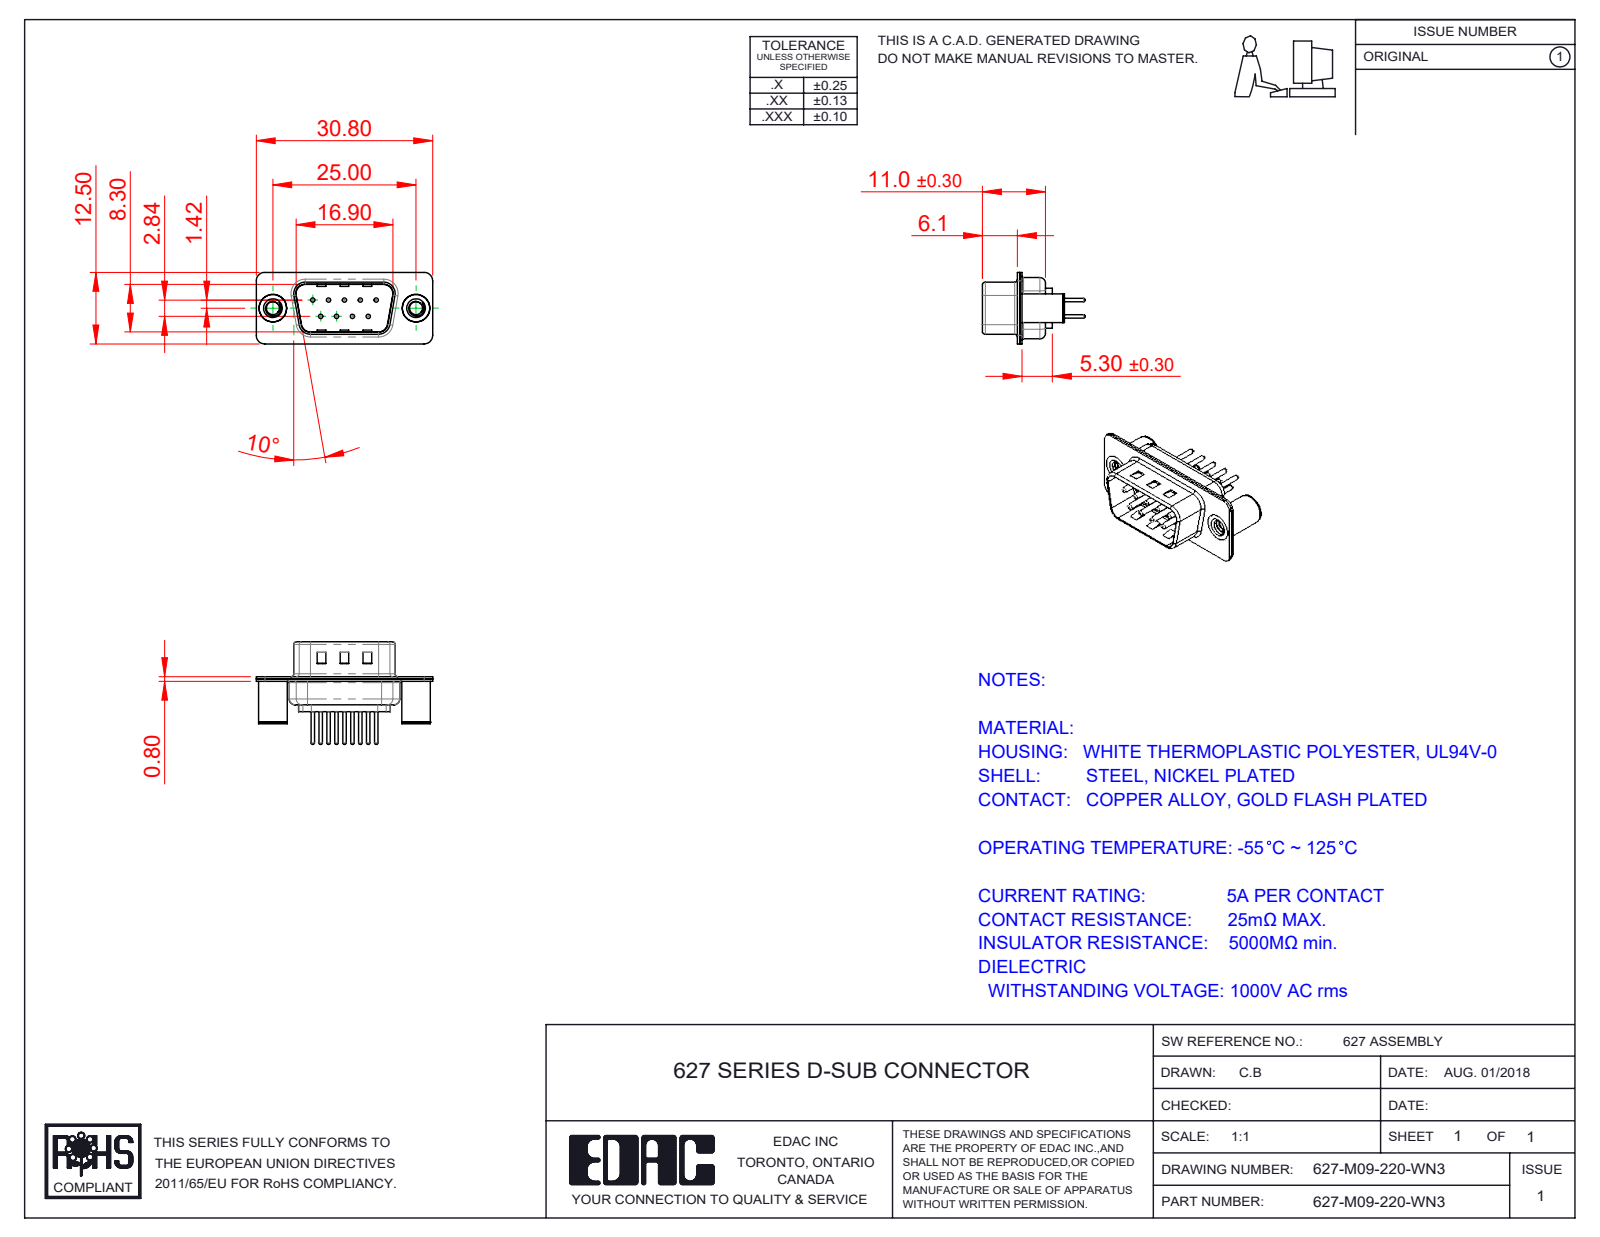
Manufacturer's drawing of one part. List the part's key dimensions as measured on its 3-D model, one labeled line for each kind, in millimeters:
Part name (STEP PRODUCT): 627M Shell Rear_09 Contacts; 627M Contact Row 1_20; 627-M09-220-WN3; 627M Shell Front_09 Contacts (+3 more)
STEP written by: SolidWorks 2020 (CONFIG_CONTROL_DESIGN)
Units: millimetres
Bodies: 14 solids, 671 faces (170 planar, 279 cylindrical, 222 other)
Overall size (bounding box): 30.8 × 17.9 × 12.5
Volume: 1 433 mm³ · Surface area: 3 832 mm²
Round holes (diameter × count): ⌀0.75 ×9, ⌀1.6 ×9, ⌀2 ×9, ⌀2.26 ×2, ⌀3.26 ×2, ⌀4 ×2, ⌀4.8 ×2
Round bosses / shafts (diameter × count): ⌀1.5 ×9, ⌀0.6 ×9, ⌀5 ×2, ⌀4.9 ×2
Partial cylindrical surfaces — rounded edges, fillets, slot ends (radius × count): R1.5 ×16, R2 ×12, R0.5 ×8, R1.6 ×8, R0.25 ×4, R0.6 ×4, R0.65 ×4, R0.9 ×4
Main face-to-face distances: 0.4, 0.8, 9.5, 9.1, 8.7, 0.65, 9.9, 1.2, 5.3, 6.1
Hole centre spacings: 3.16, 2.77, 5.54, 5.03, 5.04, 8.31, 7.1, 7.48
